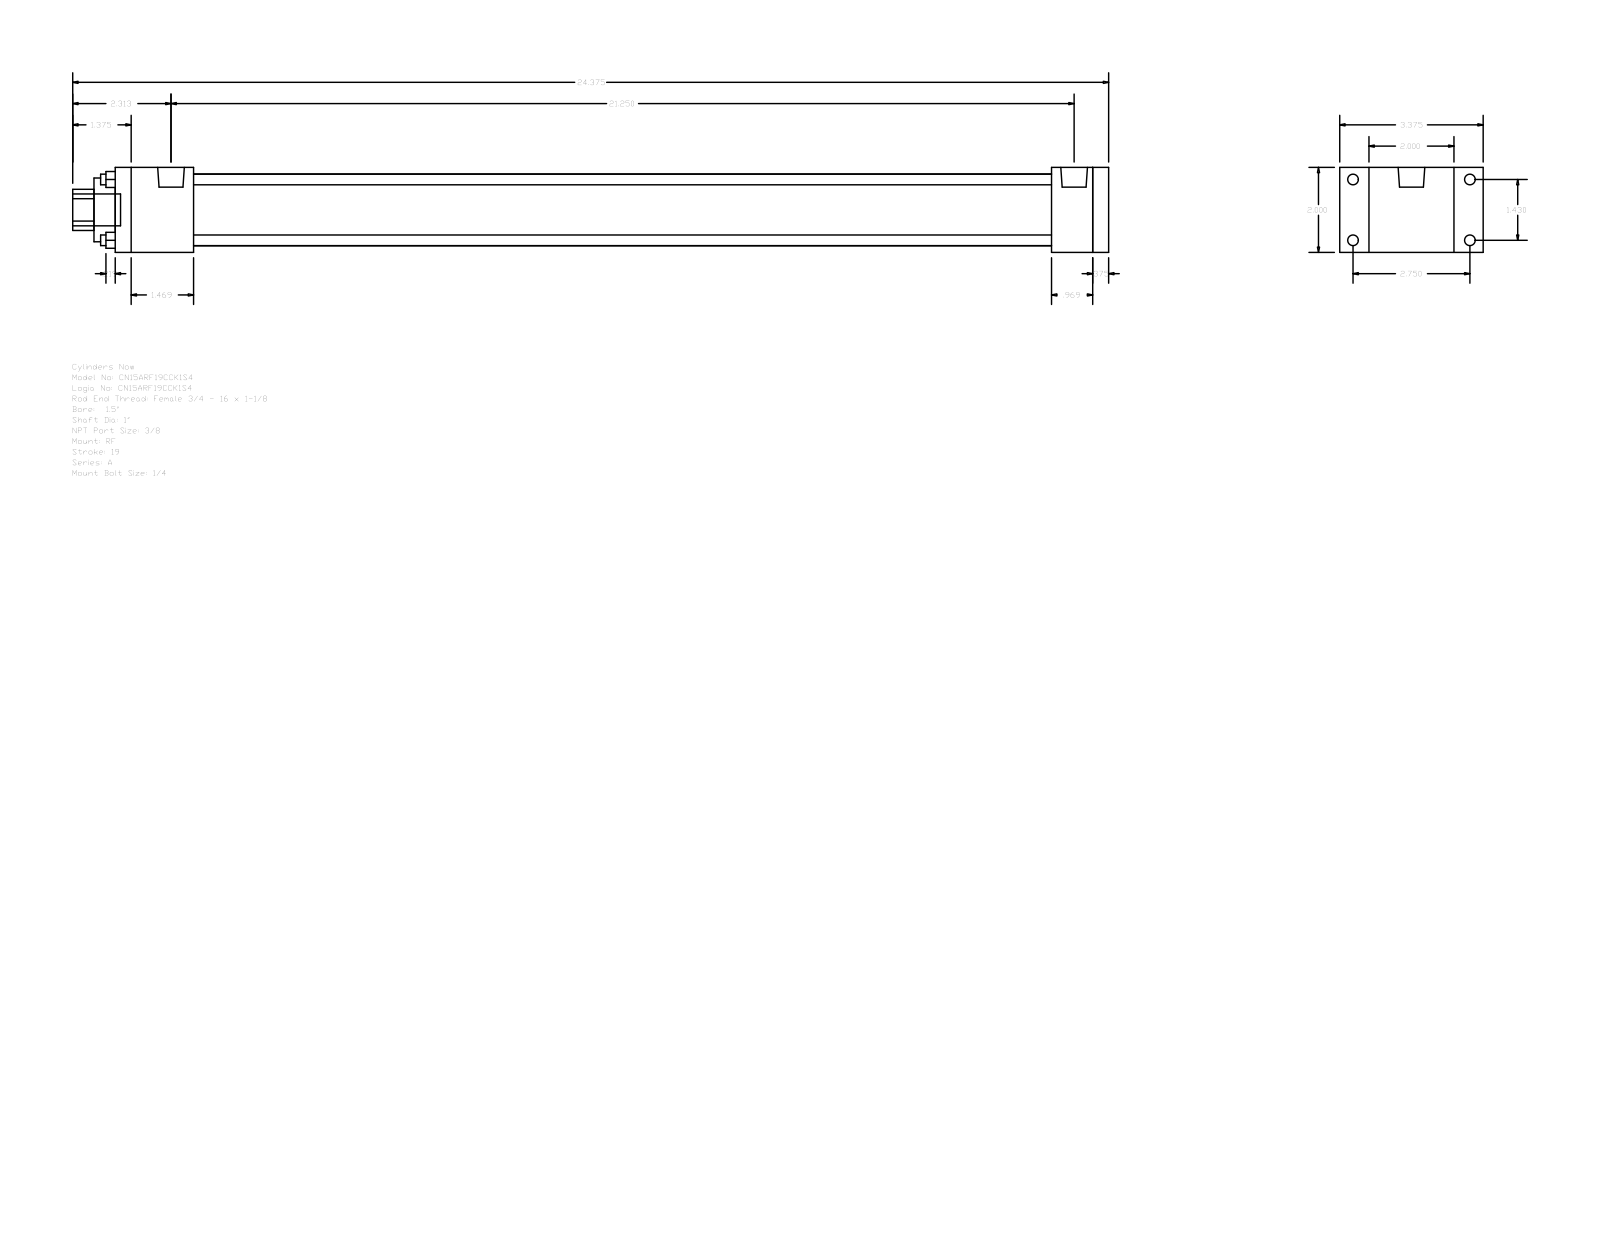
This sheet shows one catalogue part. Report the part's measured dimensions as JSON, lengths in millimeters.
{"part_name": "A_RF__0150_1", "step_written_by": "GSSL Pune (CONFIG_CONTROL_DESIGN)", "units": "millimeters", "bodies": {"solids": 0, "faces": 92, "planar": 64, "cylindrical": 28, "other": 0}, "overall_size": [619.12, 85.72, 50.8], "round_holes": [[6.35, 4], [25.4, 1], [38.1, 1], [42.93, 1]], "round_bosses_or_shafts": [[6.35, 4], [5.56, 4], [15.93, 2], [19.05, 1]], "partial_cylinders_radius": [[12.29, 1]], "face_to_face_distances": [50.8, 9.52, 584.2, 593.72, 559.59, 24.61, 34.13, 46.83, 512.76, 537.37], "hole_center_spacings": [25.68, 36.32, 51.36]}
